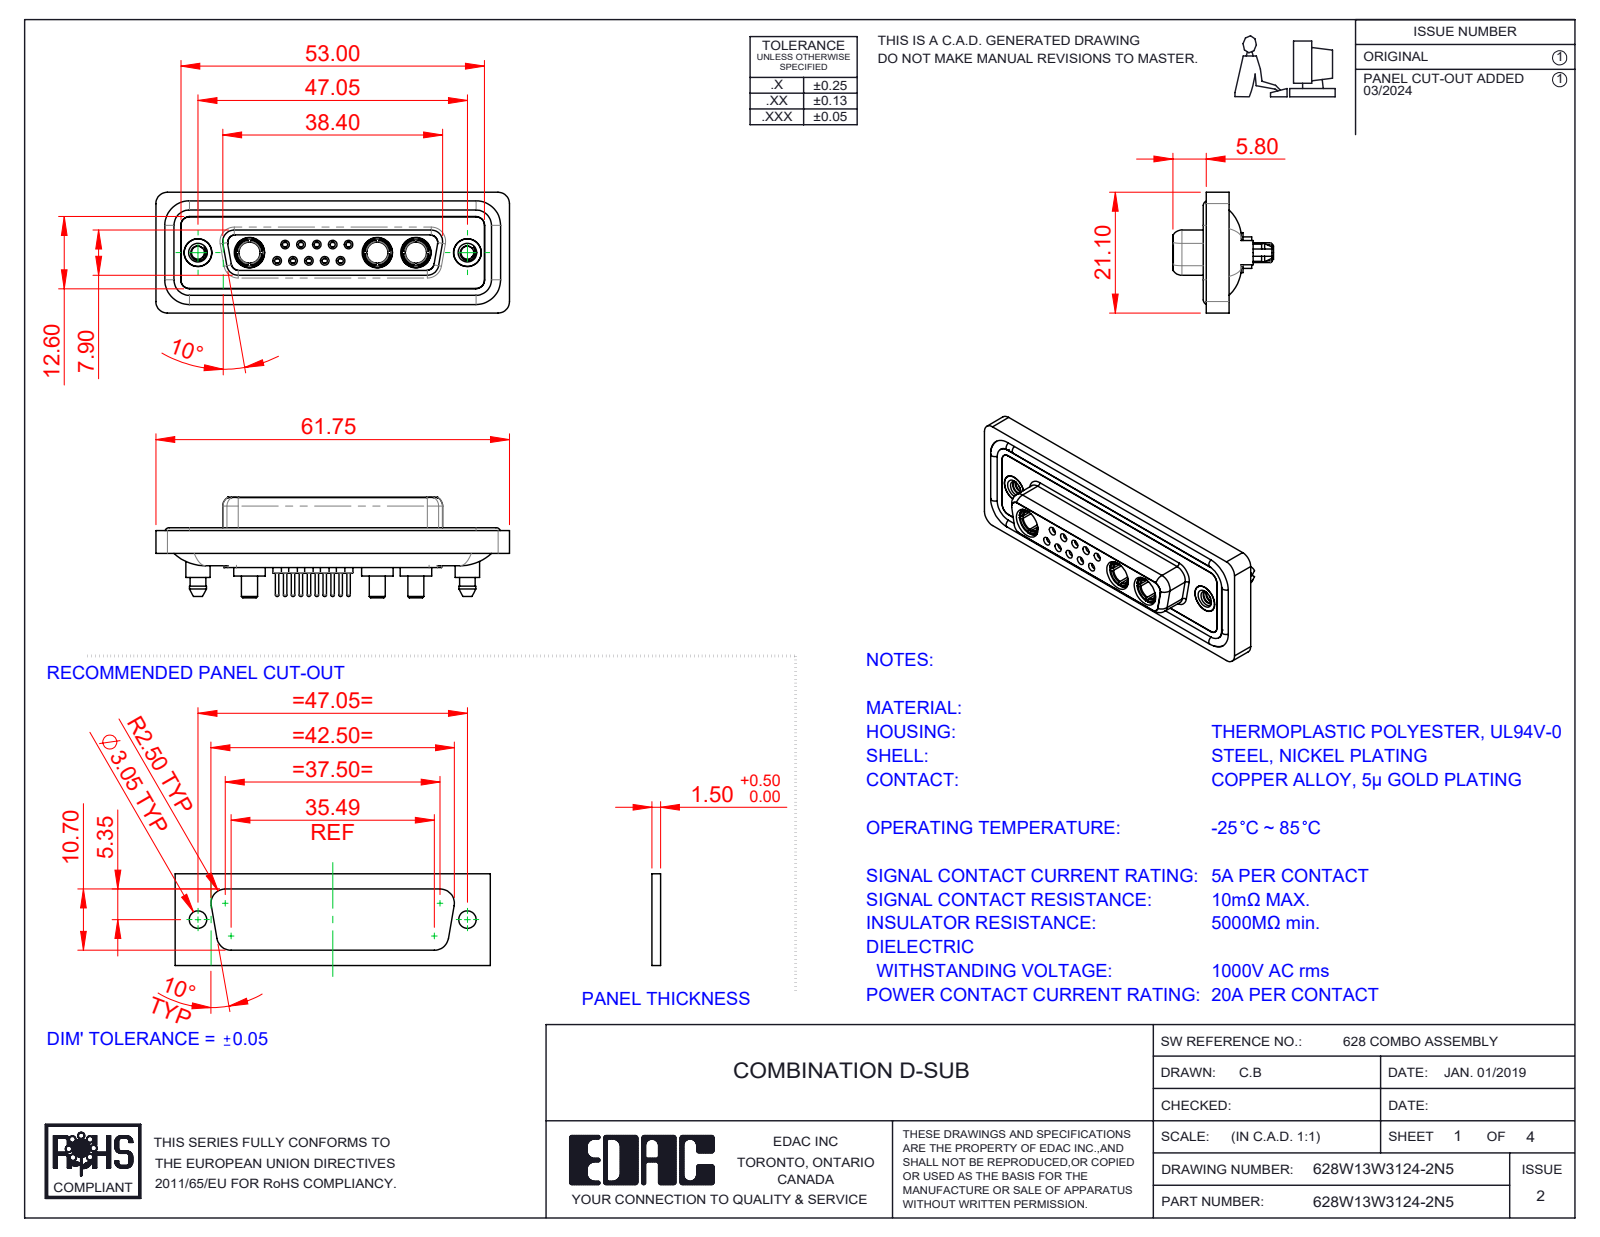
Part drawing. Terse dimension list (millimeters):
name: 628Combo Contact Row 1_24; 628Combo Waterproof Housing_25 Contacts; 628W13W3124-2N5; Power Socket_20A S (+5 more)
written by: SolidWorks 2023 (CONFIG_CONTROL_DESIGN)
unit: mm
bodies: 23 solids, 1208 faces (358 planar, 479 cylindrical, 371 other)
size: 61.75 × 21.1 × 17.55
volume: 8 407 mm³; area: 14 042 mm²
holes: 10× ⌀0.9, 10× ⌀1.1, 10× ⌀1.5, 10× ⌀2, 5× ⌀1.6, 5× ⌀1.7, 5× ⌀4.85, 3× ⌀3.7, 3× ⌀5.3, 2× ⌀2.26, 2× ⌀4, 2× ⌀4.05
bosses: 10× ⌀2.2, 10× ⌀0.6, 9× ⌀1.6, 3× ⌀5.5, 3× ⌀5.2, 3× ⌀4.96, 3× ⌀4.75, 3× ⌀3.75
rounds: 24× R1.5, 18× R2, 10× R1.6, 8× R1.35, 4× R0.25, 4× R0.5, 4× R0.6, 4× R0.65
face distances: 0.4, 1.8, 7.45, 5.65, 0.5, 6.6, 7.05, 1.6, 2.9, 1.1
hole spacings: 3.16, 2.77, 5.03, 5.04, 5.54, 8.31, 7.49, 2.76
